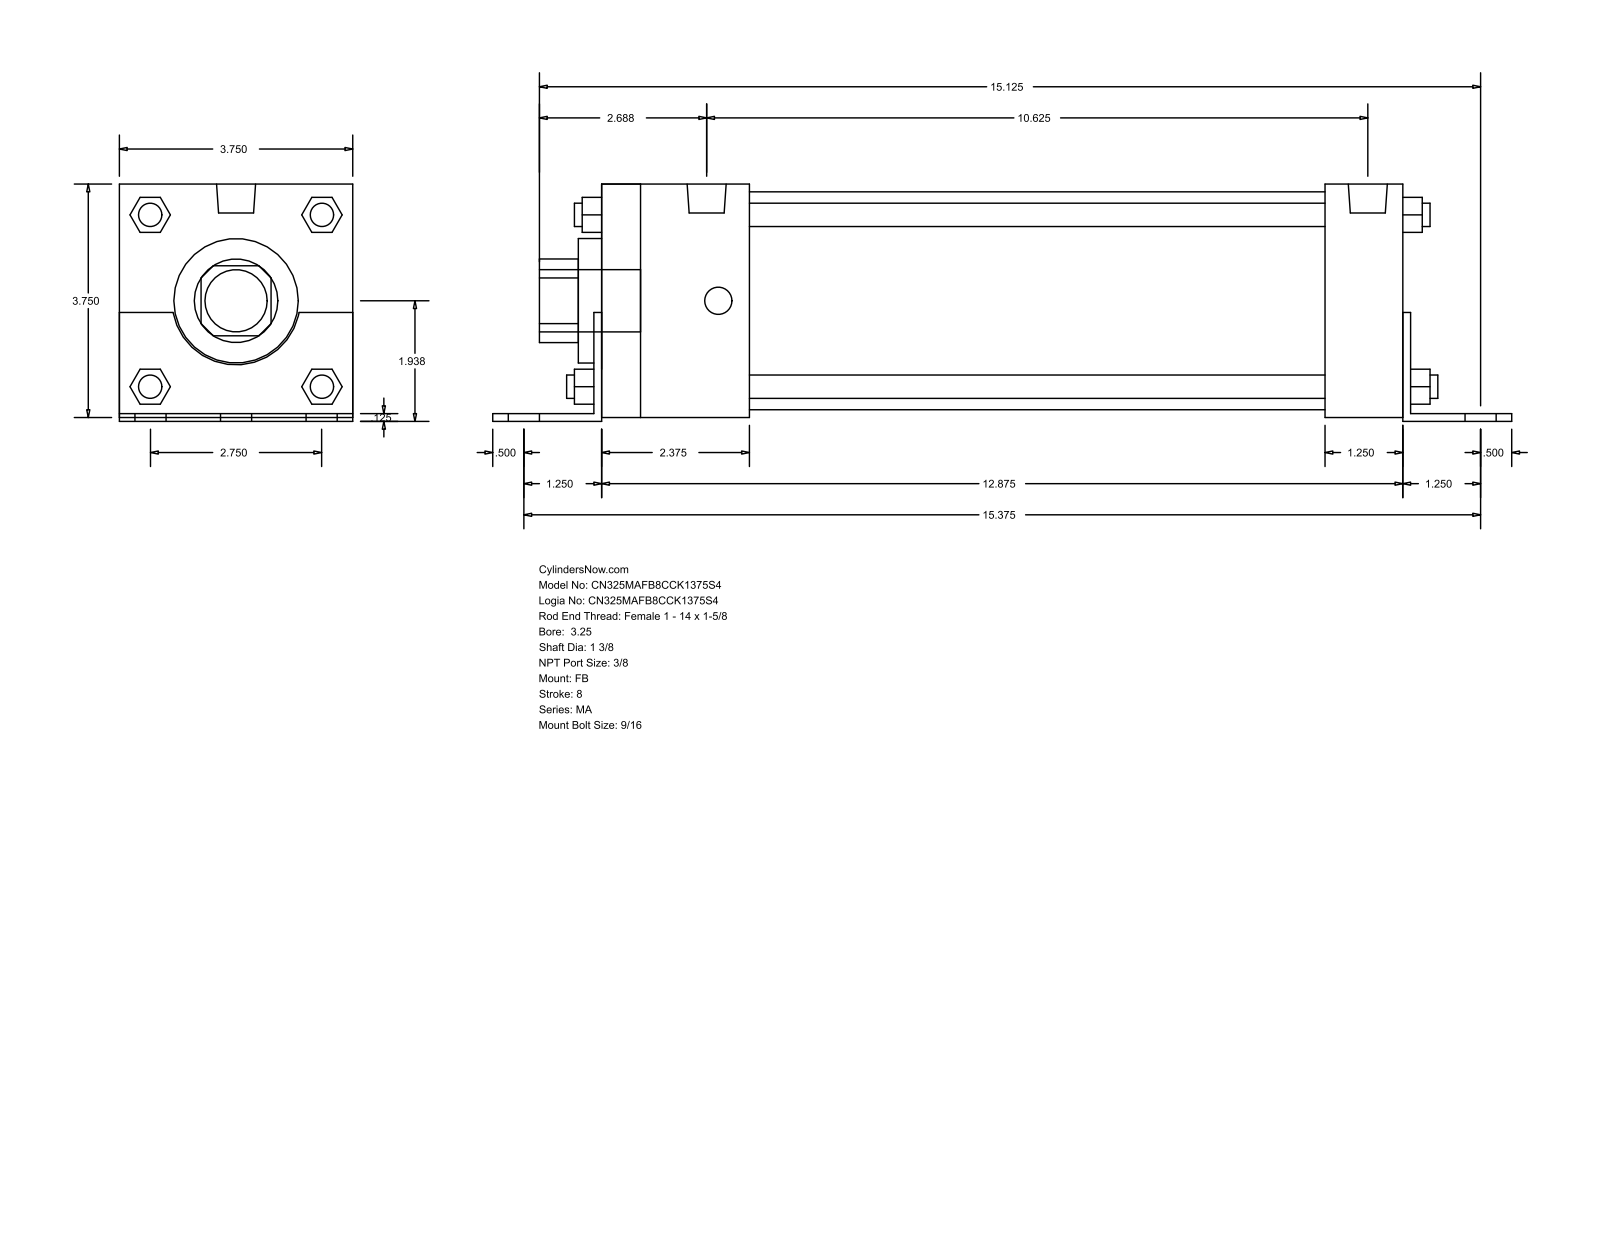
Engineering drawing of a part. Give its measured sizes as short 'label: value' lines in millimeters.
name: MA_FB__0325_1.375
written by: GSSL Pune (CONFIG_CONTROL_DESIGN)
unit: mm
bodies: 0 solids, 140 faces (105 planar, 35 cylindrical, 0 other)
size: 415.93 × 96.84 × 95.25
holes: 1× ⌀34.92, 1× ⌀50.8, 1× ⌀88.9
bosses: 6× ⌀14.29, 4× ⌀11.11, 4× ⌀9.53, 2× ⌀15.93, 1× ⌀25.4
rounds: 1× R17.06, 1× R26.16
face distances: 95.24, 3.17, 1.59, 96.83, 1.58, 93.66, 330.2, 327.03, 31.75, 60.32
